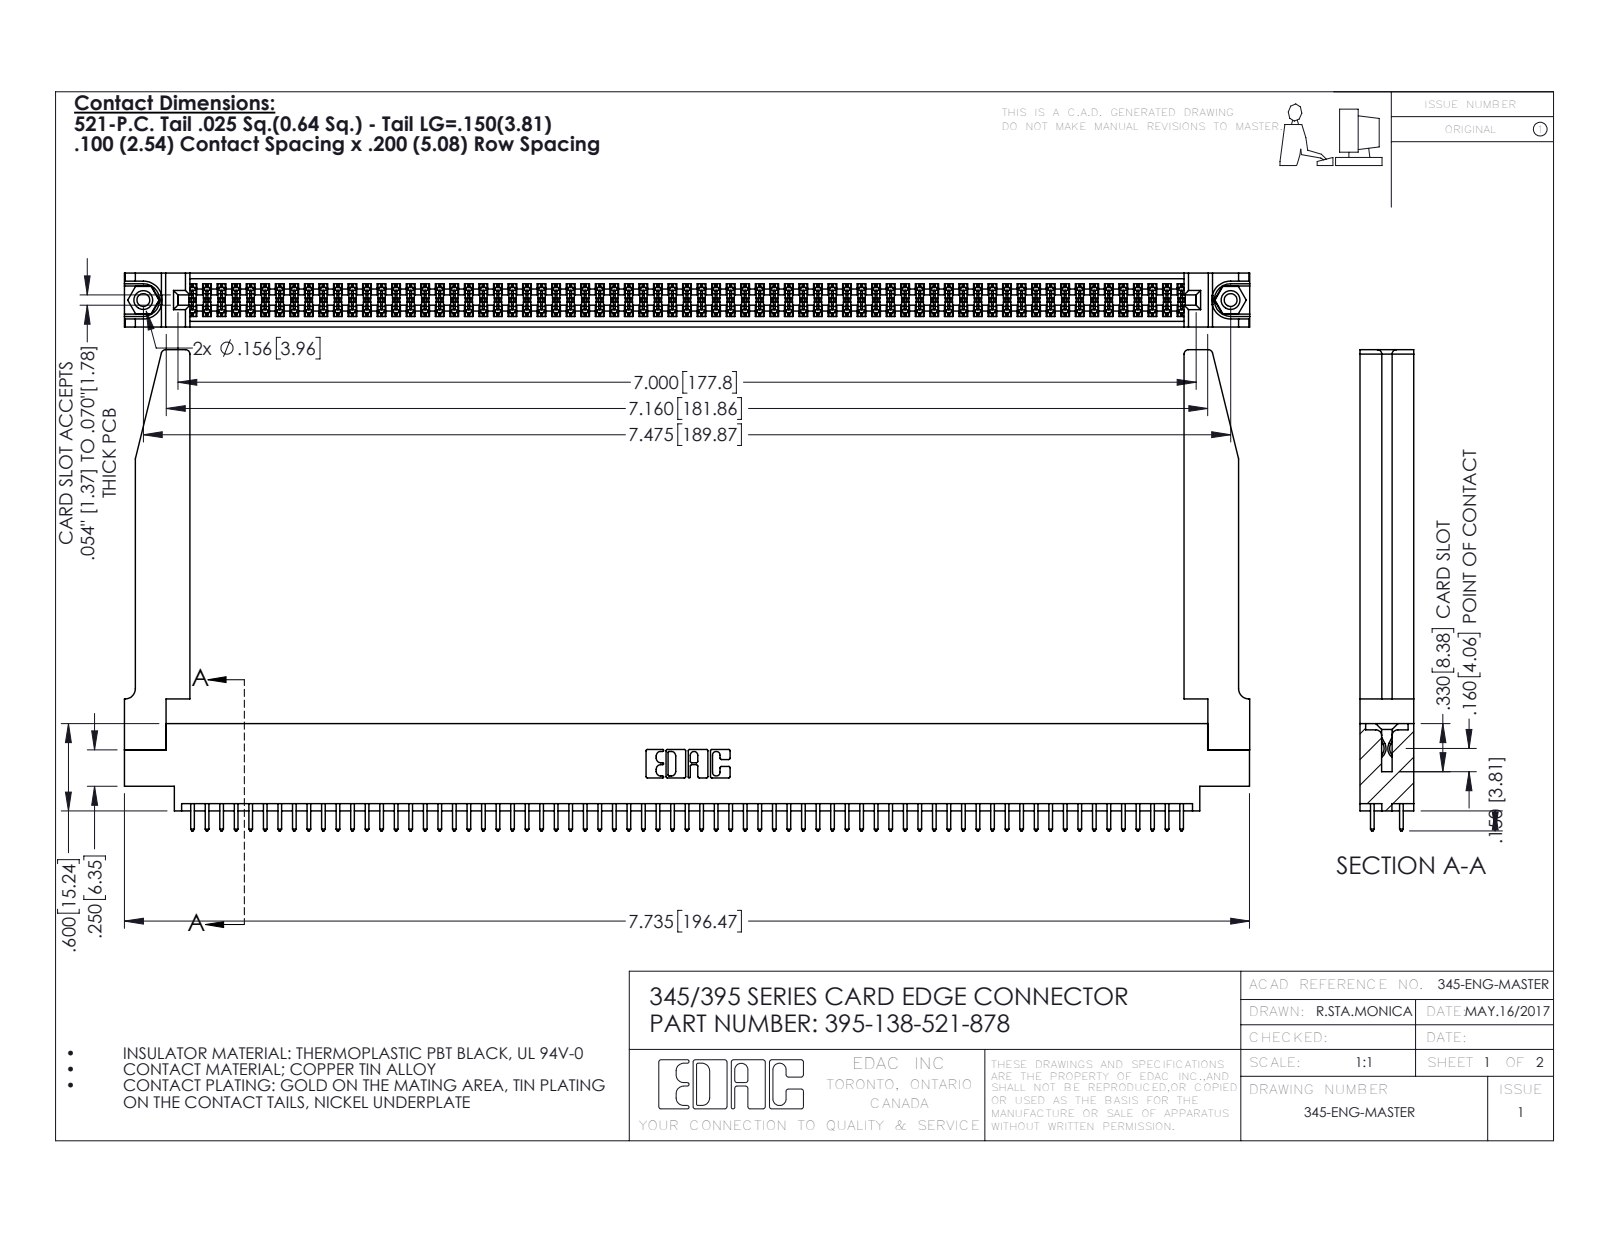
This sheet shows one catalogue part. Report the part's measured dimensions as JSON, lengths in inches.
{"part_name": "395-138-521-878; 345-220-078_345-220-078; 345 Part_0.170 Offset - 0.156 Dia-TH; 345-292-001_345-293-121 (+1 more)", "step_written_by": "SolidWorks 2016 (CONFIG_CONTROL_DESIGN)", "units": "inches", "bodies": {"solids": 143, "faces": 7264, "planar": 4780, "cylindrical": 2432, "other": 52}, "overall_size": [7.736, 3.307, 0.37], "volume_in3": 1.644, "surface_area_in2": 54.98, "round_holes": [[0.089, 2], [0.125, 2], [0.156, 2], [0.064, 1]], "round_bosses_or_shafts": [[0.155, 2]], "partial_cylinders_radius": [[0.006, 207], [0.01, 138], [0.01, 22], [0.03, 8], [0.007, 6], [0.031, 6], [0.026, 3], [0.014, 2]], "face_to_face_distances": [0.072, 0.298, 0.37, 0.098, 0.272, 0.025, 0.2, 0.225, 0.175, 0.149], "hole_center_spacings": [0.27, 7.239, 7.475]}
